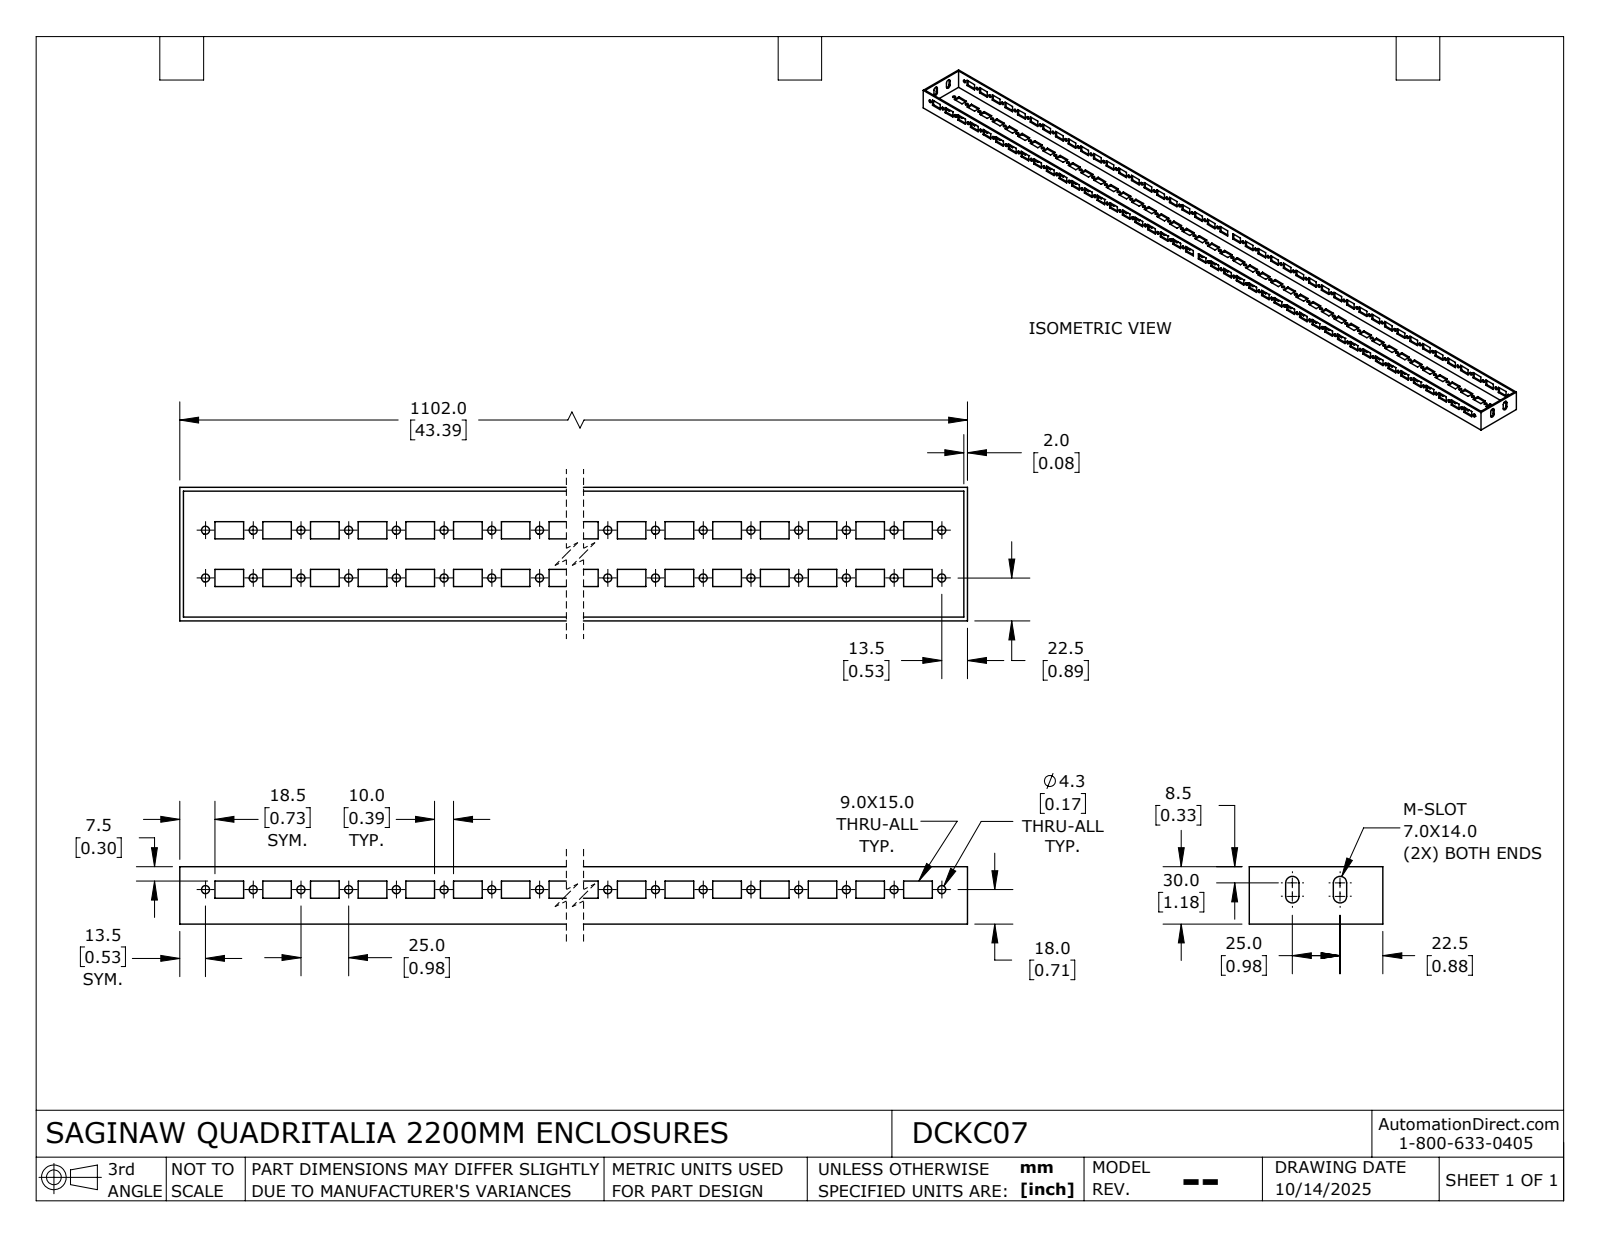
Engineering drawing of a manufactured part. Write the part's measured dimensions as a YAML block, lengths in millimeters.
part_name: "DCKC07_Default"
step_written_by: "SolidWorks 2024 (CONFIG_CONTROL_DESIGN)"
units: millimeters
bodies: {solids: 1, faces: 889, planar: 707, cylindrical: 182, other: 0}
overall_size: [1102, 70, 30]
volume: 233019
surface_area: 259154
round_holes:
  - {diameter: 4.25, count: 131}
partial_cylinders:
  - {radius: 3.5, count: 4}
face_to_face_distances: [2, 68, 70, 66, 25, 9, 30, 28, 16, 50]
hole_center_spacings: [25, 50, 75, 100, 125, 150, 175, 200]
